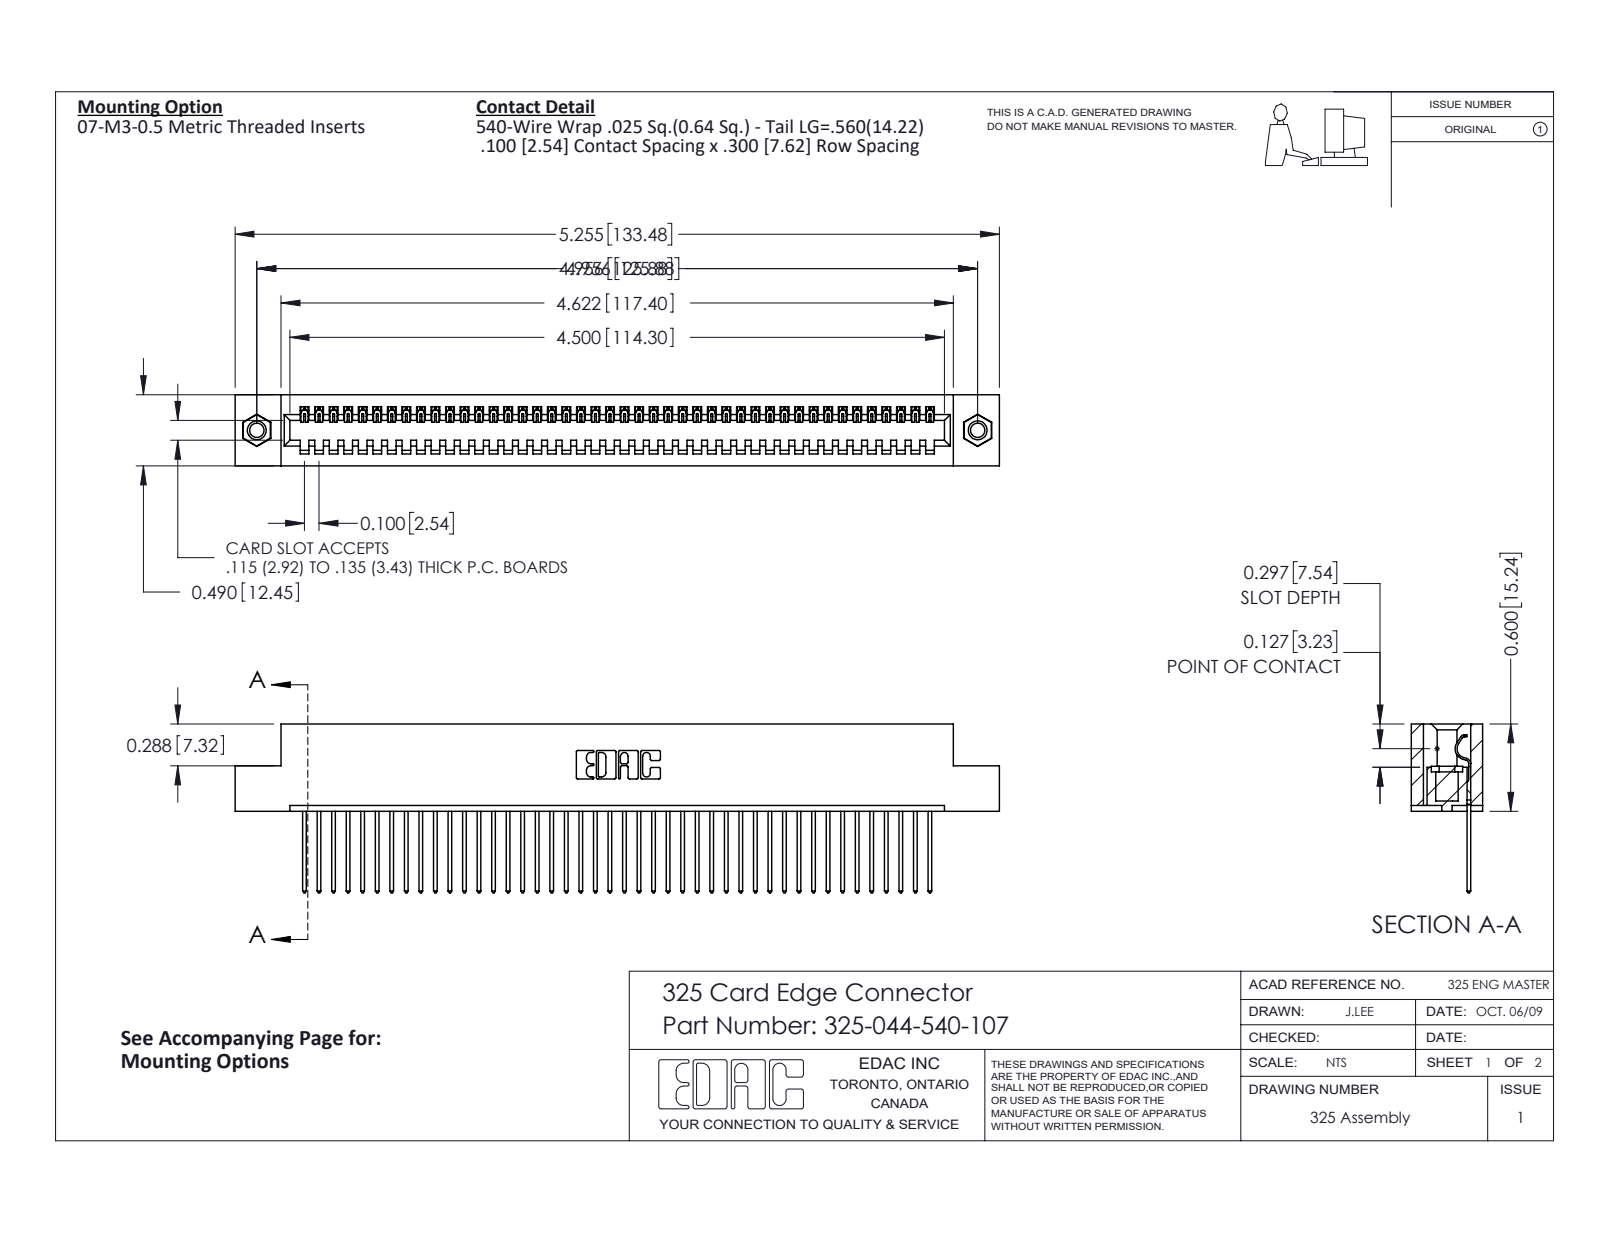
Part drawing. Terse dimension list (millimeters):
name: 325-292-001_325-293-140; 325-044-540-107; 345-250-001_345-250-005-103; 325 Part_TI
written by: SolidWorks 2016 (CONFIG_CONTROL_DESIGN)
unit: mm
bodies: 47 solids, 2726 faces (1950 planar, 760 cylindrical, 16 other)
size: 133.5 × 29.5 × 12.4
volume: 17 010 mm³; area: 19 080 mm²
holes: 2× ⌀2.5, 2× ⌀3.2, 2× ⌀4.1
bosses: 2× ⌀3.9
rounds: 88× R0.2, 88× R0.3, 22× R0.3, 6× R0.2, 6× R0.8, 3× R0.7, 1× R0.4, 1× R0.6
face distances: 2.1, 10.3, 12.4, 7.6, 2.7, 9.7, 0.6, 8.3, 14.2, 1
hole spacings: 125.9
